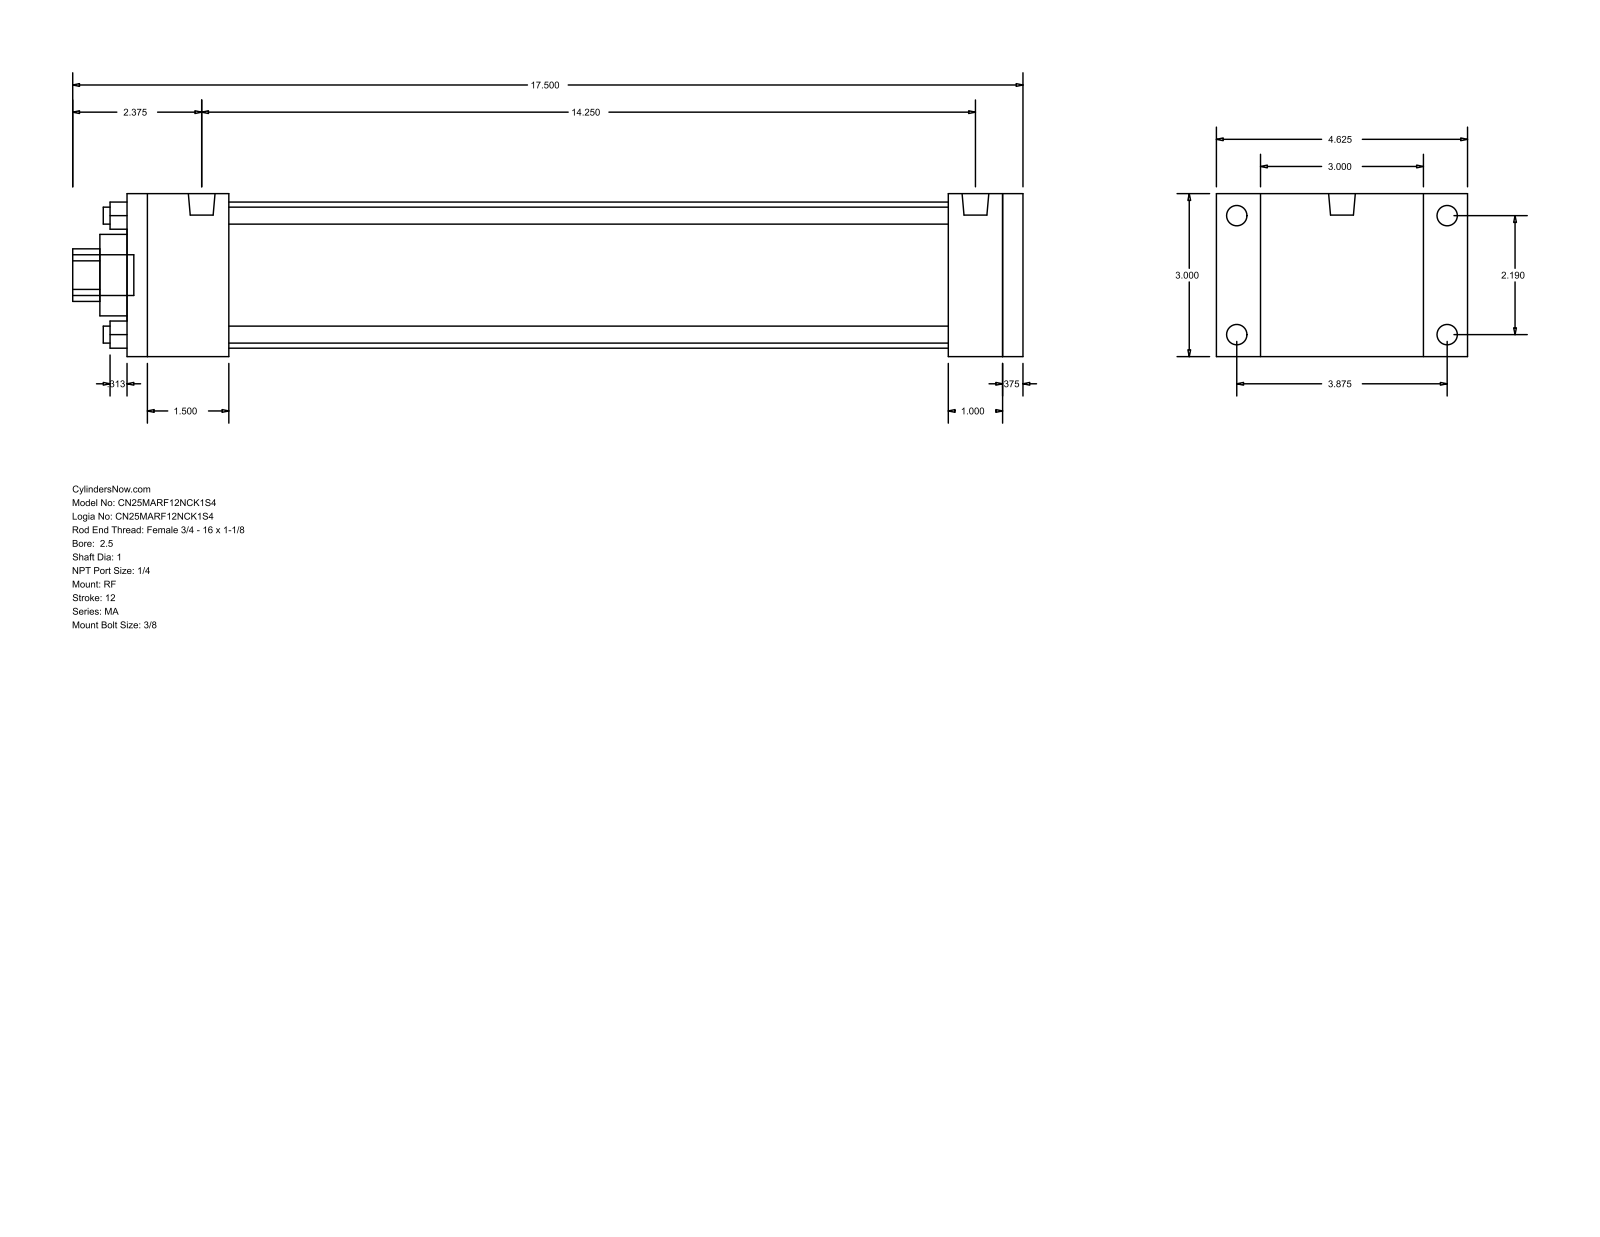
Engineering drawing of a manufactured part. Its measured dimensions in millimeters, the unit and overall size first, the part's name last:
Units: millimetres
Overall size (bounding box): 444.5 × 117.47 × 76.2
Round holes (diameter × count): ⌀7.94 ×4, ⌀25.4 ×1, ⌀38.1 ×1, ⌀68.33 ×1
Round bosses / shafts (diameter × count): ⌀9.53 ×4, ⌀7.94 ×4, ⌀12.49 ×2, ⌀19.05 ×1
Partial cylindrical surfaces — rounded edges, fillets, slot ends (radius × count): R12.29 ×1
Main face-to-face distances: 76.2, 419.1, 409.58, 9.52, 47.63, 384.17, 336.54, 361.95, 371.47, 25.41
Hole centre spacings: 39.33, 55.62, 78.66
Bodies: 0 solids, 92 faces (64 planar, 28 cylindrical, 0 other)
Part name (STEP PRODUCT): MA_RF__0250_1
STEP written by: GSSL Pune (CONFIG_CONTROL_DESIGN)
